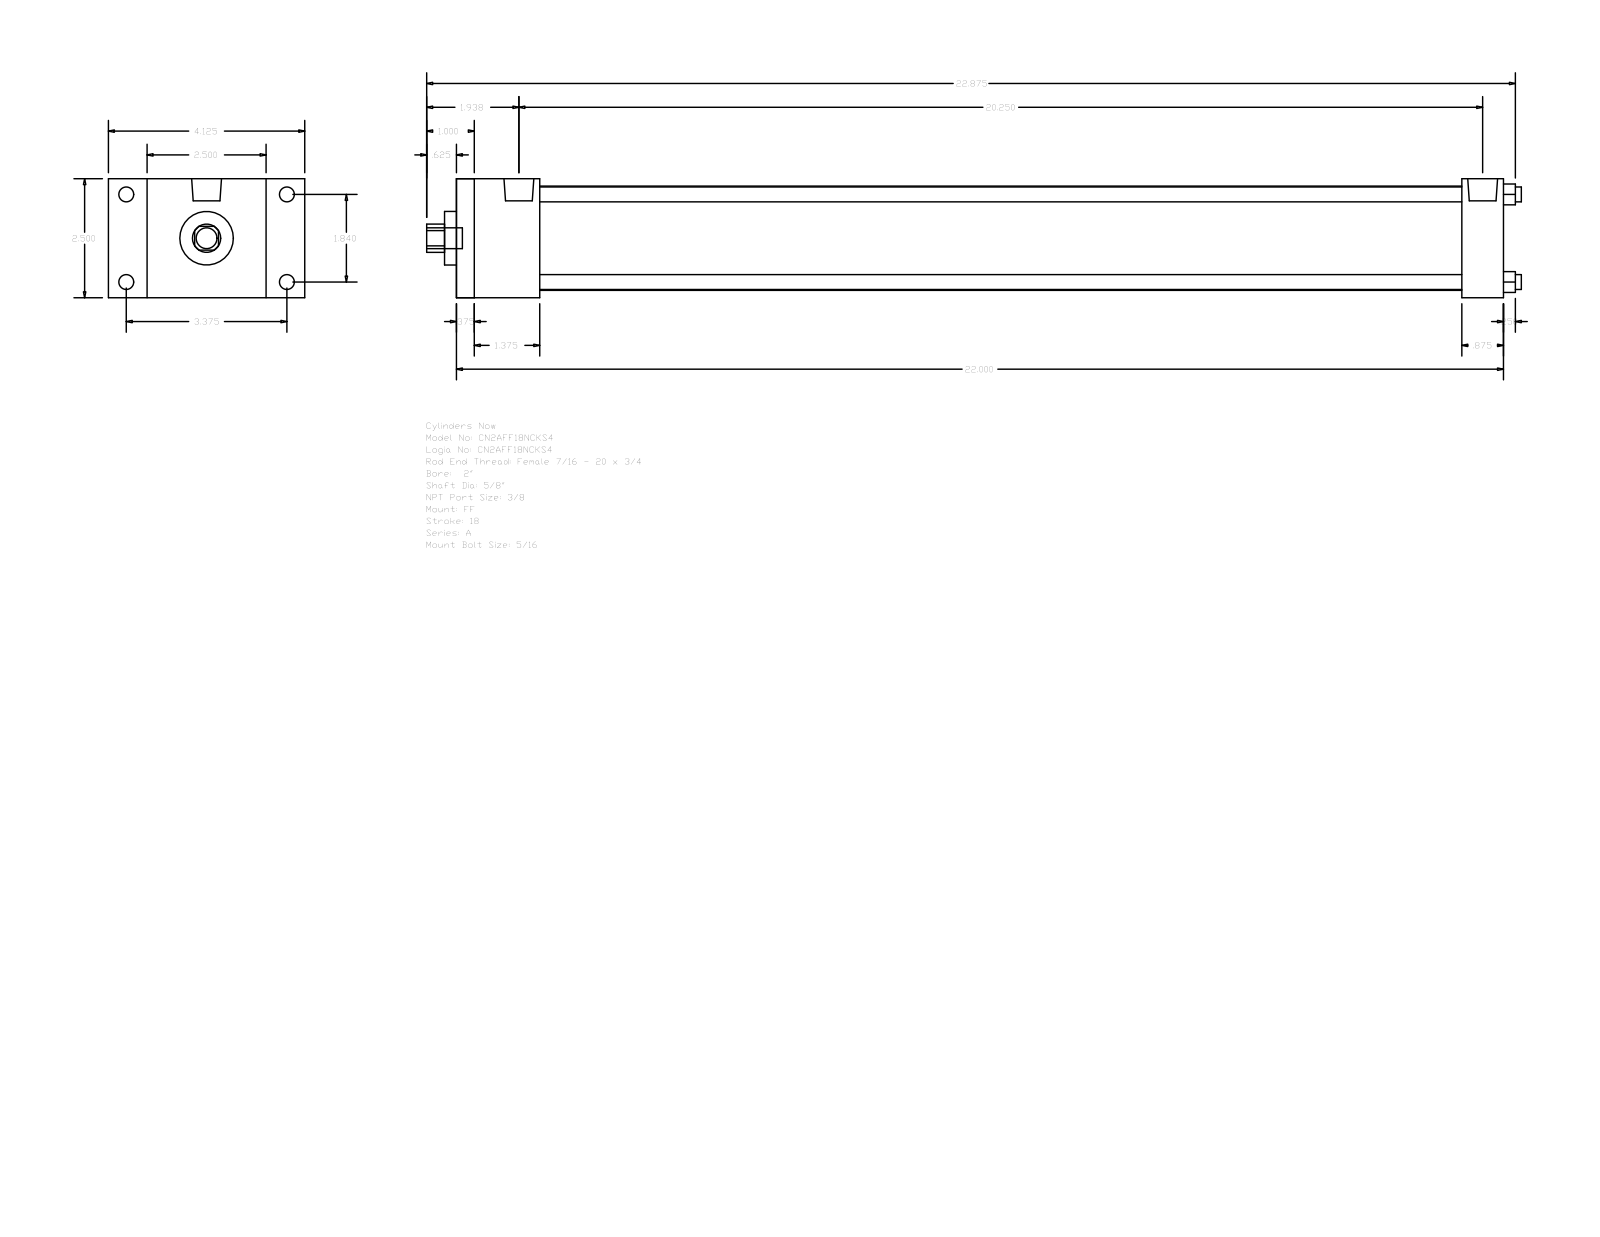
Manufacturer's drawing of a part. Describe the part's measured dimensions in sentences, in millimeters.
The part is named "A_FF__0200_0.625". Its 3-D file was written by "GSSL Pune (CONFIG_CONTROL_DESIGN)". It is 0 solids with 92 faces: 64 planar, 28 cylindrical and 0 other. Overall it measures 584.2 by 104.78 by 63.5 millimeters. Round holes: 4 of diameter 7.94, 1 of diameter 15.88, 1 of diameter 28.57, 1 of diameter 55.63. Round bosses or shafts: 4 of diameter 7.94, 4 of diameter 5.56, 2 of diameter 15.93, 1 of diameter 11.11. Partial cylindrical surfaces (rounded edges, fillets, slot ends): 1 of radius 7.54. The main face-to-face distances are 63.5, 558.79, 9.52, 549.27, 44.45, 536.57, 34.93, 527.05, 492.12, 514.34. The hole center spacings are 33.05, 46.74, 66.1.
